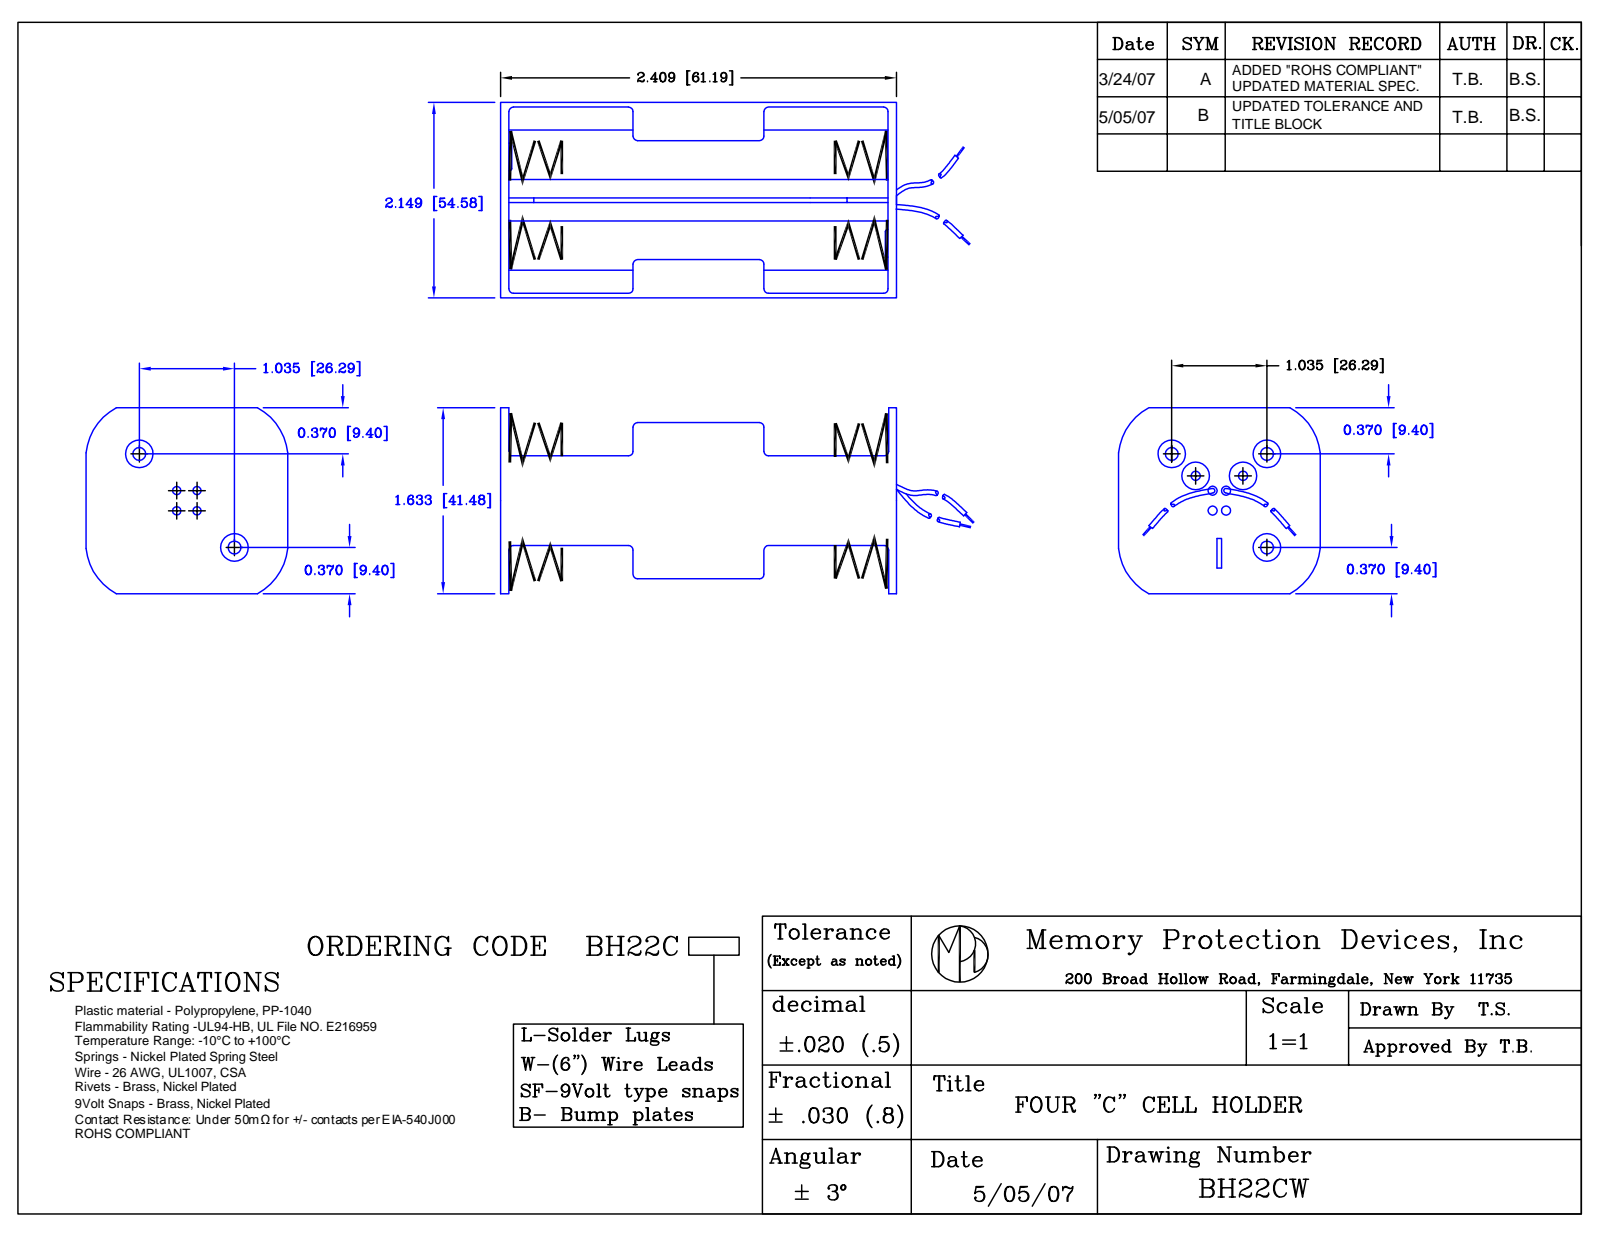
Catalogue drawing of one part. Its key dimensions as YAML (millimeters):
part_name: "BH22CW"
step_written_by: "SolidWorks 2017 (AUTOMOTIVE_DESIGN)"
units: millimeters
bodies: {solids: 16, faces: 420, planar: 143, cylindrical: 177, other: 100}
overall_size: [216.19, 54.58, 41.48]
volume: 18211
surface_area: 26273
round_holes:
  - {diameter: 4.44, count: 5}
  - {diameter: 1.5, count: 4}
  - {diameter: 10.16, count: 3}
  - {diameter: 0.4, count: 2}
  - {diameter: 2.54, count: 2}
  - {diameter: 7.62, count: 2}
  - {diameter: 8.89, count: 1}
round_bosses_or_shafts:
  - {diameter: 6.35, count: 6}
  - {diameter: 8.25, count: 4}
  - {diameter: 0.76, count: 4}
  - {diameter: 1.14, count: 2}
  - {diameter: 0.81, count: 2}
  - {diameter: 4.44, count: 1}
partial_cylinders:
  - {radius: 0.5, count: 16}
  - {radius: 3.81, count: 8}
  - {radius: 8.63, count: 4}
  - {radius: 9.27, count: 4}
  - {radius: 10.16, count: 4}
  - {radius: 3.5, count: 1}
  - {radius: 5, count: 1}
face_to_face_distances: [1.52, 26.53, 28.05, 59.67, 1.53, 53.06, 25.01, 58.14, 61.19, 59.66]
hole_center_spacings: [26.28, 3.02, 4.54, 5.45, 5.92, 8.52, 9.39, 9.77]
